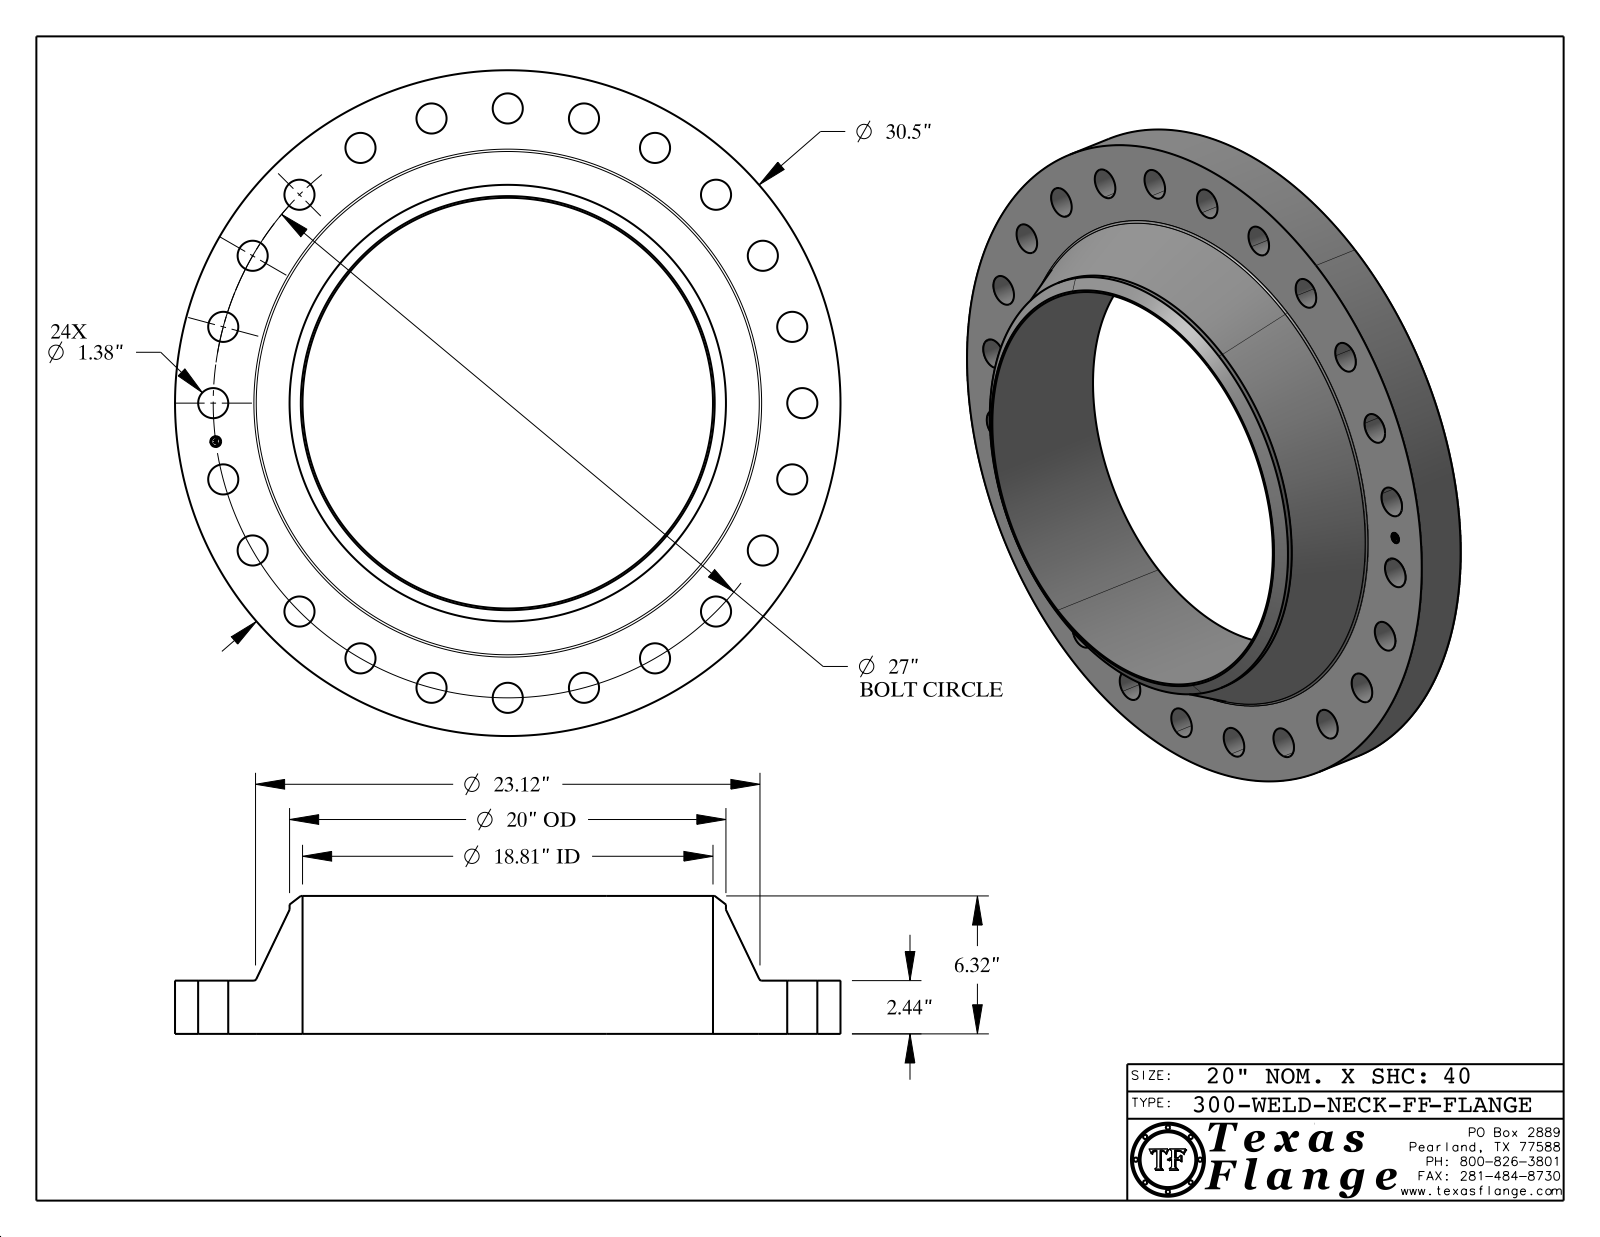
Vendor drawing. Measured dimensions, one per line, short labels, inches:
name: 300-WELD-NECK-FF
written by: CATIA V5 STEP AP214 (AUTOMOTIVE_DESIGN)
unit: in
bodies: 1 solid, 449 faces (369 planar, 74 cylindrical, 6 other)
size: 30.5 × 30.5 × 6.32
volume: 1 319 in³; area: 1 855 in²
holes: 24× ⌀1.38, 1× ⌀0.495, 1× ⌀18.812
bosses: 8× ⌀0.03, 1× ⌀30.5, 1× ⌀20, 1× ⌀0.39
face distances: 2.44, 6.32, 3.88, 2.425, 0.015, 3.895, 0.148, 0.144, 0.027, 0.096
hole spacings: 13.5, 3.524, 6.988, 10.333, 16.437, 24.945, 26.769, 21.421
